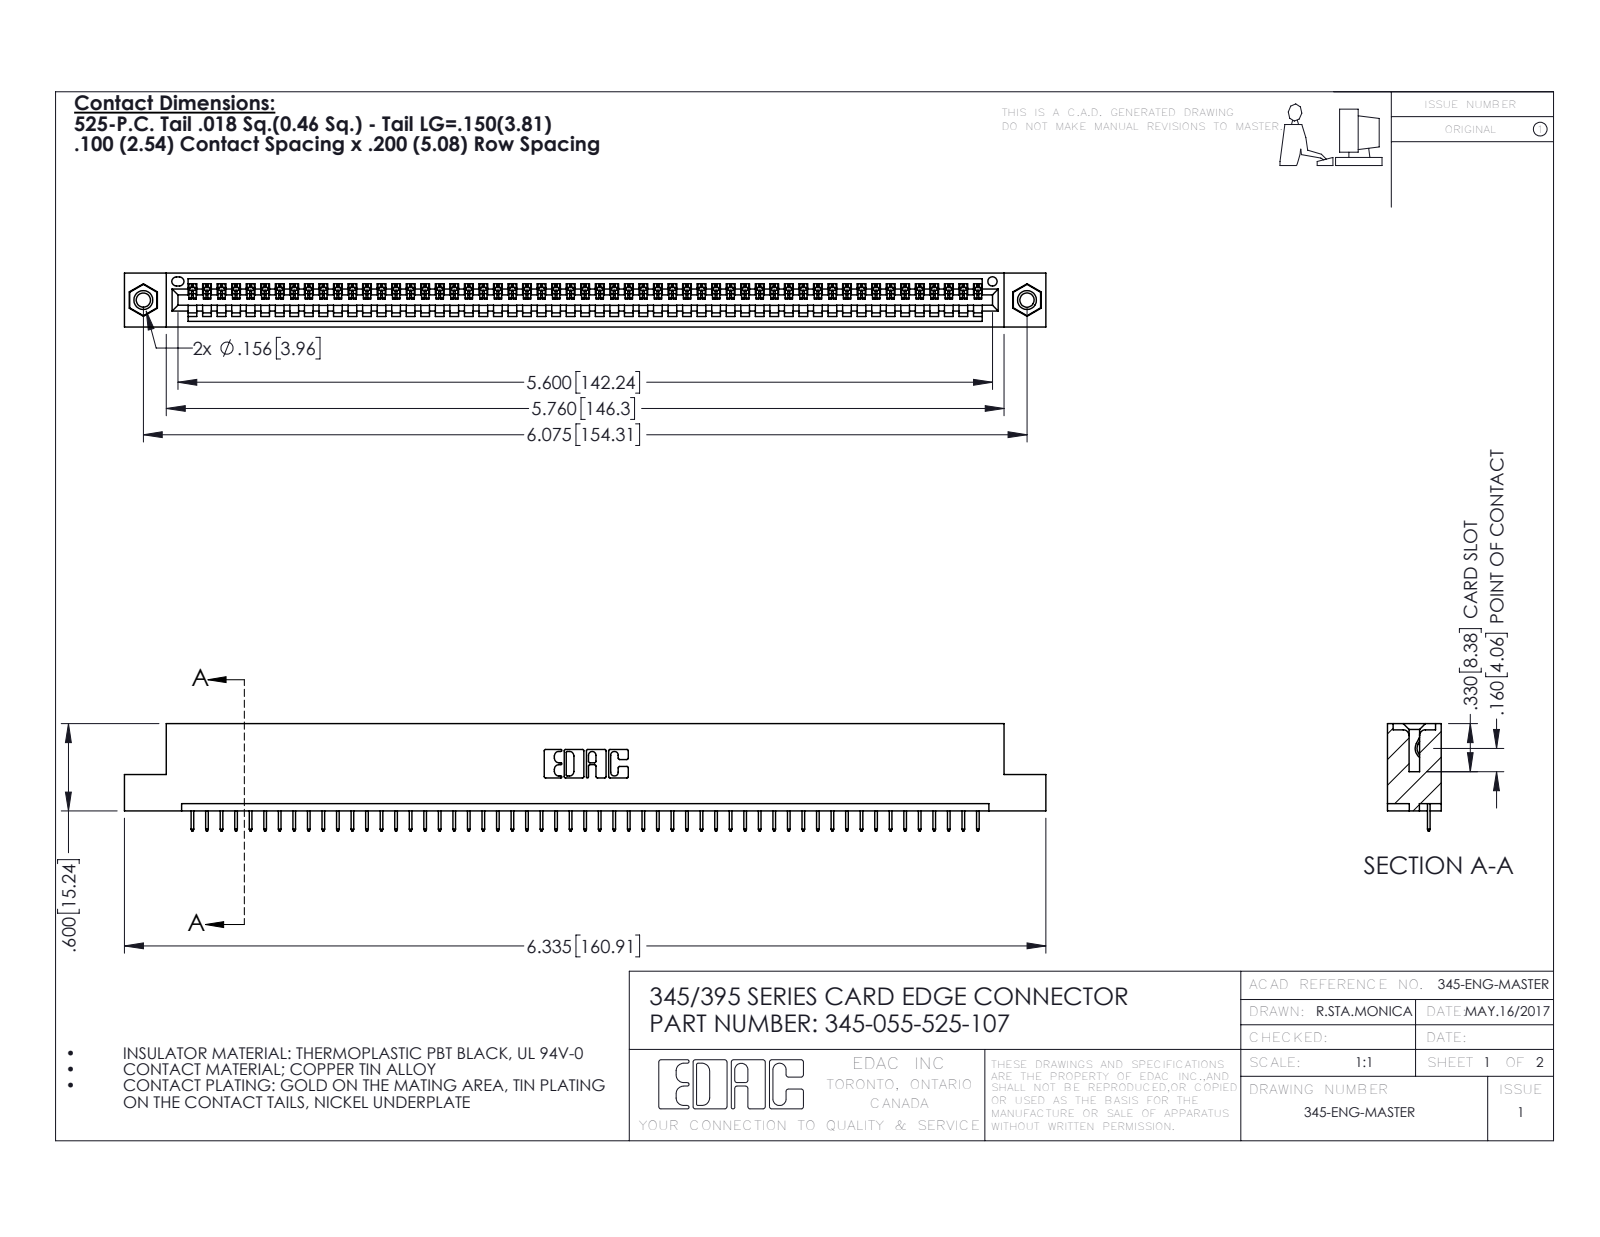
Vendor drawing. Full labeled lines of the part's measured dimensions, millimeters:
Part name (STEP PRODUCT): 345-250-001_345-250-005-103; 345-292-001_345-293-125; 345-055-525-107; 345 Part_Flush Mounting Lugs - 0.156 Dia-TI
STEP written by: SolidWorks 2020 (CONFIG_CONTROL_DESIGN)
Units: millimetres
Bodies: 58 solids, 3596 faces (2642 planar, 938 cylindrical, 16 other)
Overall size (bounding box): 160.9 × 18.7 × 9.4
Volume: 15 200 mm³ · Surface area: 19 590 mm²
Round holes (diameter × count): ⌀2.5 ×2, ⌀3.2 ×2, ⌀4 ×2, ⌀1.6 ×1
Round bosses / shafts (diameter × count): ⌀3.9 ×2
Partial cylindrical surfaces — rounded edges, fillets, slot ends (radius × count): R0.2 ×110, R0.3 ×22, R0.2 ×6, R0.8 ×6, R0.7 ×3, R0.8 ×2, R1 ×2, R0.4 ×1
Main face-to-face distances: 1.8, 7.6, 9.4, 5.1, 2.5, 6.9, 0.6, 5.7, 1.8, 3.8
Hole centre spacings: 6.9, 148.3, 154.3
